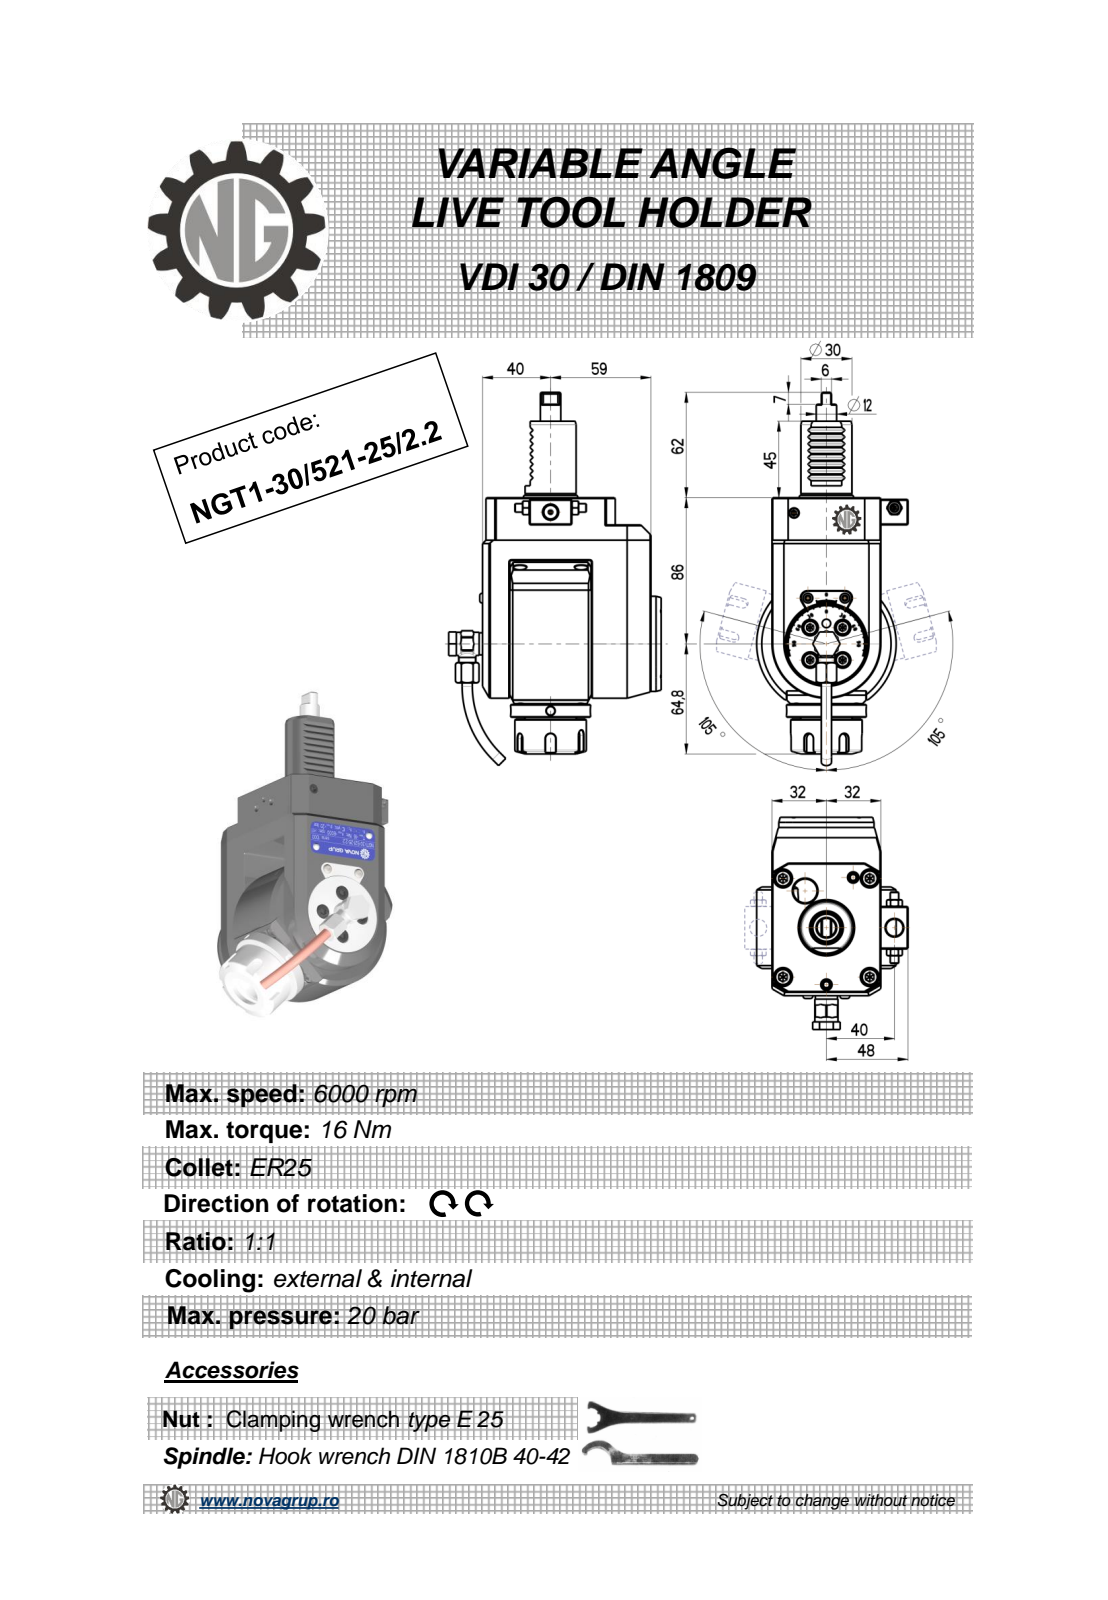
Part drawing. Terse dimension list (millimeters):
name: NGT1_30_521_25_2_2
written by: PRO/ENGINEER BY PARAMETRIC TECHNOLOGY CORPORATION, 2010280 (CONFIG_CONTROL_DESIGN)
unit: mm
bodies: 1 solid, 552 faces (235 planar, 134 cylindrical, 183 other)
size: 219.67 × 124.9 × 89
volume: 796 098 mm³; area: 74 426 mm²
holes: 3× ⌀4, 2× ⌀5, 2× ⌀10, 1× ⌀3, 1× ⌀4.2, 1× ⌀6.2, 1× ⌀9, 1× ⌀9.5, 1× ⌀11, 1× ⌀20.3
bosses: 2× ⌀6, 2× ⌀5.7, 1× ⌀56, 1× ⌀47, 1× ⌀42, 1× ⌀35, 1× ⌀30, 1× ⌀13.6
rounds: 12× R0.26, 8× R0.3, 6× R0.16, 6× R0.5, 5× R3, 2× R1, 1× R7.7, 1× R32
face distances: 64, 16, 37, 6, 99, 105, 21, 14, 62, 35
hole spacings: 0.4, 39.45, 40, 49, 49.4, 63.25, 63.56, 89.44
